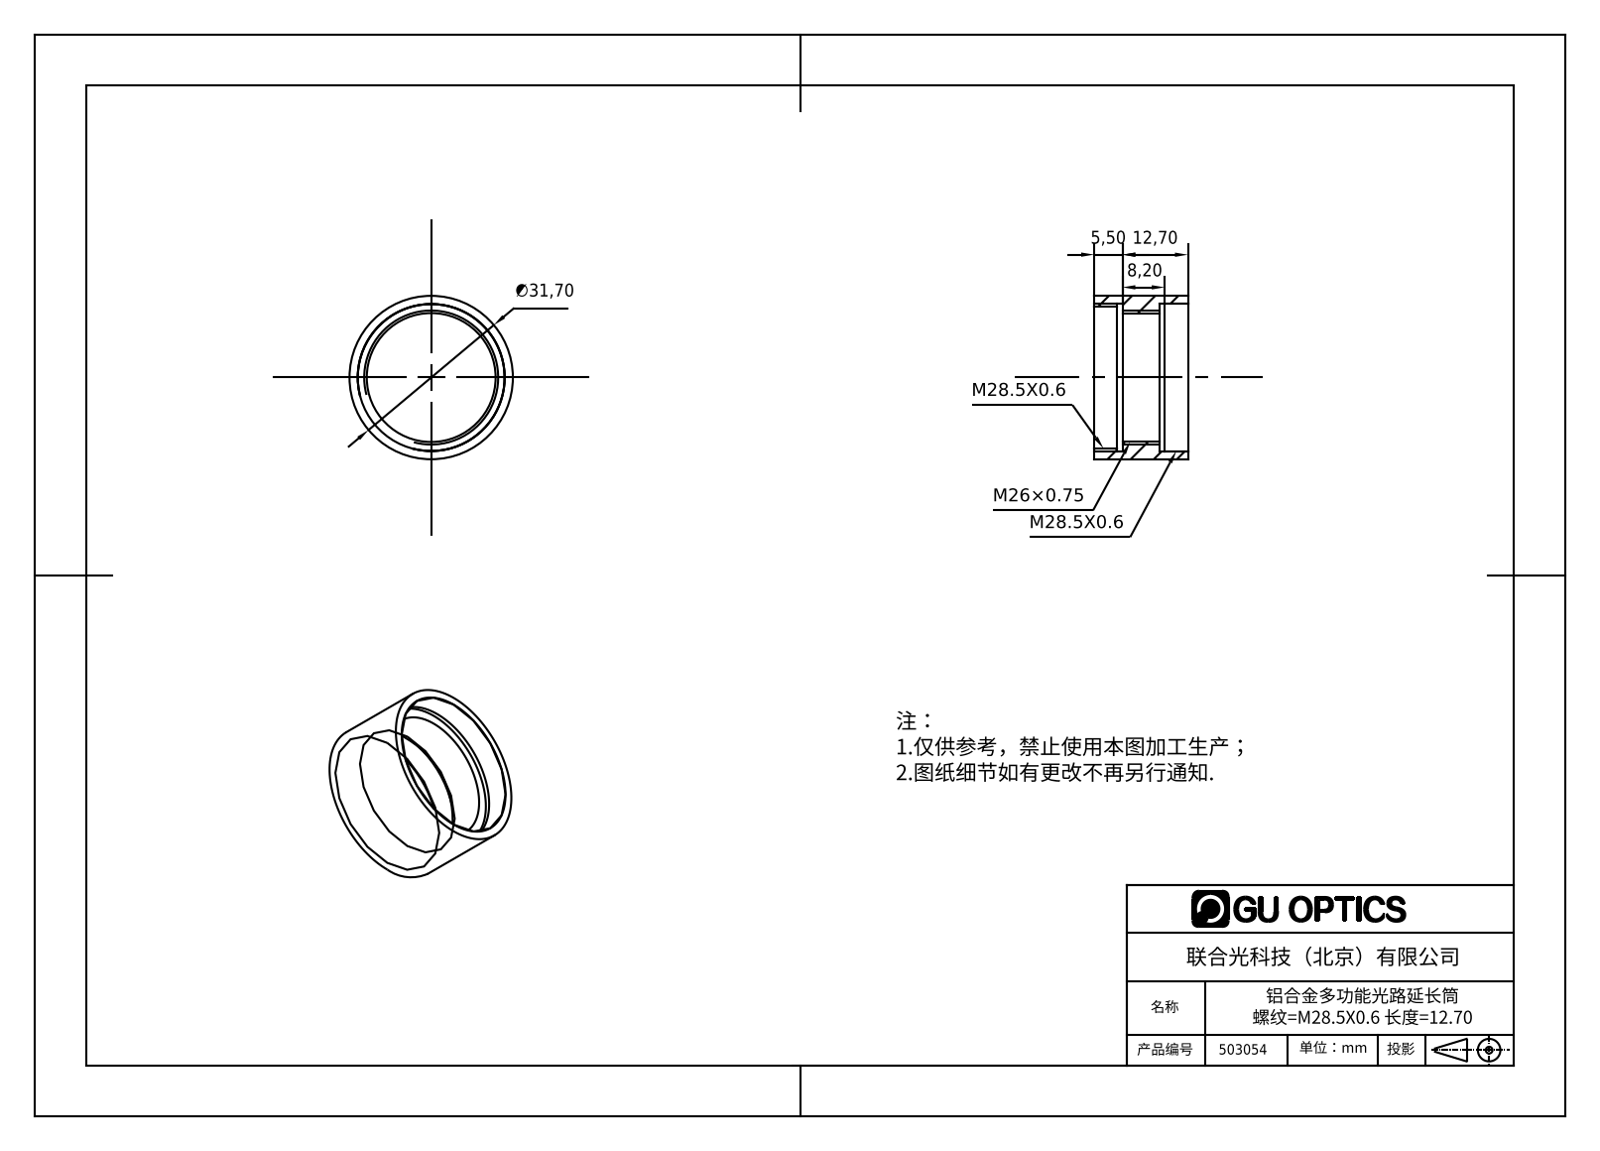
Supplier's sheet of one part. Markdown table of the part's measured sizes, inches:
| quantity | value |
| --- | --- |
| part name | 503054 |
| STEP written by | SolidWorks 2016 (AUTOMOTIVE_DESIGN) |
| units | inches |
| bodies | 1 solid, 18 faces (6 planar, 12 cylindrical, 0 other) |
| overall size | 1.248 × 1.248 × 0.717 |
| volume | 0.244 in³ |
| surface area | 6.31 in² |
| round holes (diameter × count) | 0.984 × 1, 1.083 × 1, 1.122 × 1, 1.13 × 1 |
| round bosses / shafts (diameter × count) | 1.248 × 1 |
| main face-to-face distances | 0.217, 0.5, 0.283, 0.717, 0.177, 0.539, 0.039, 0.323, 0.362 |
